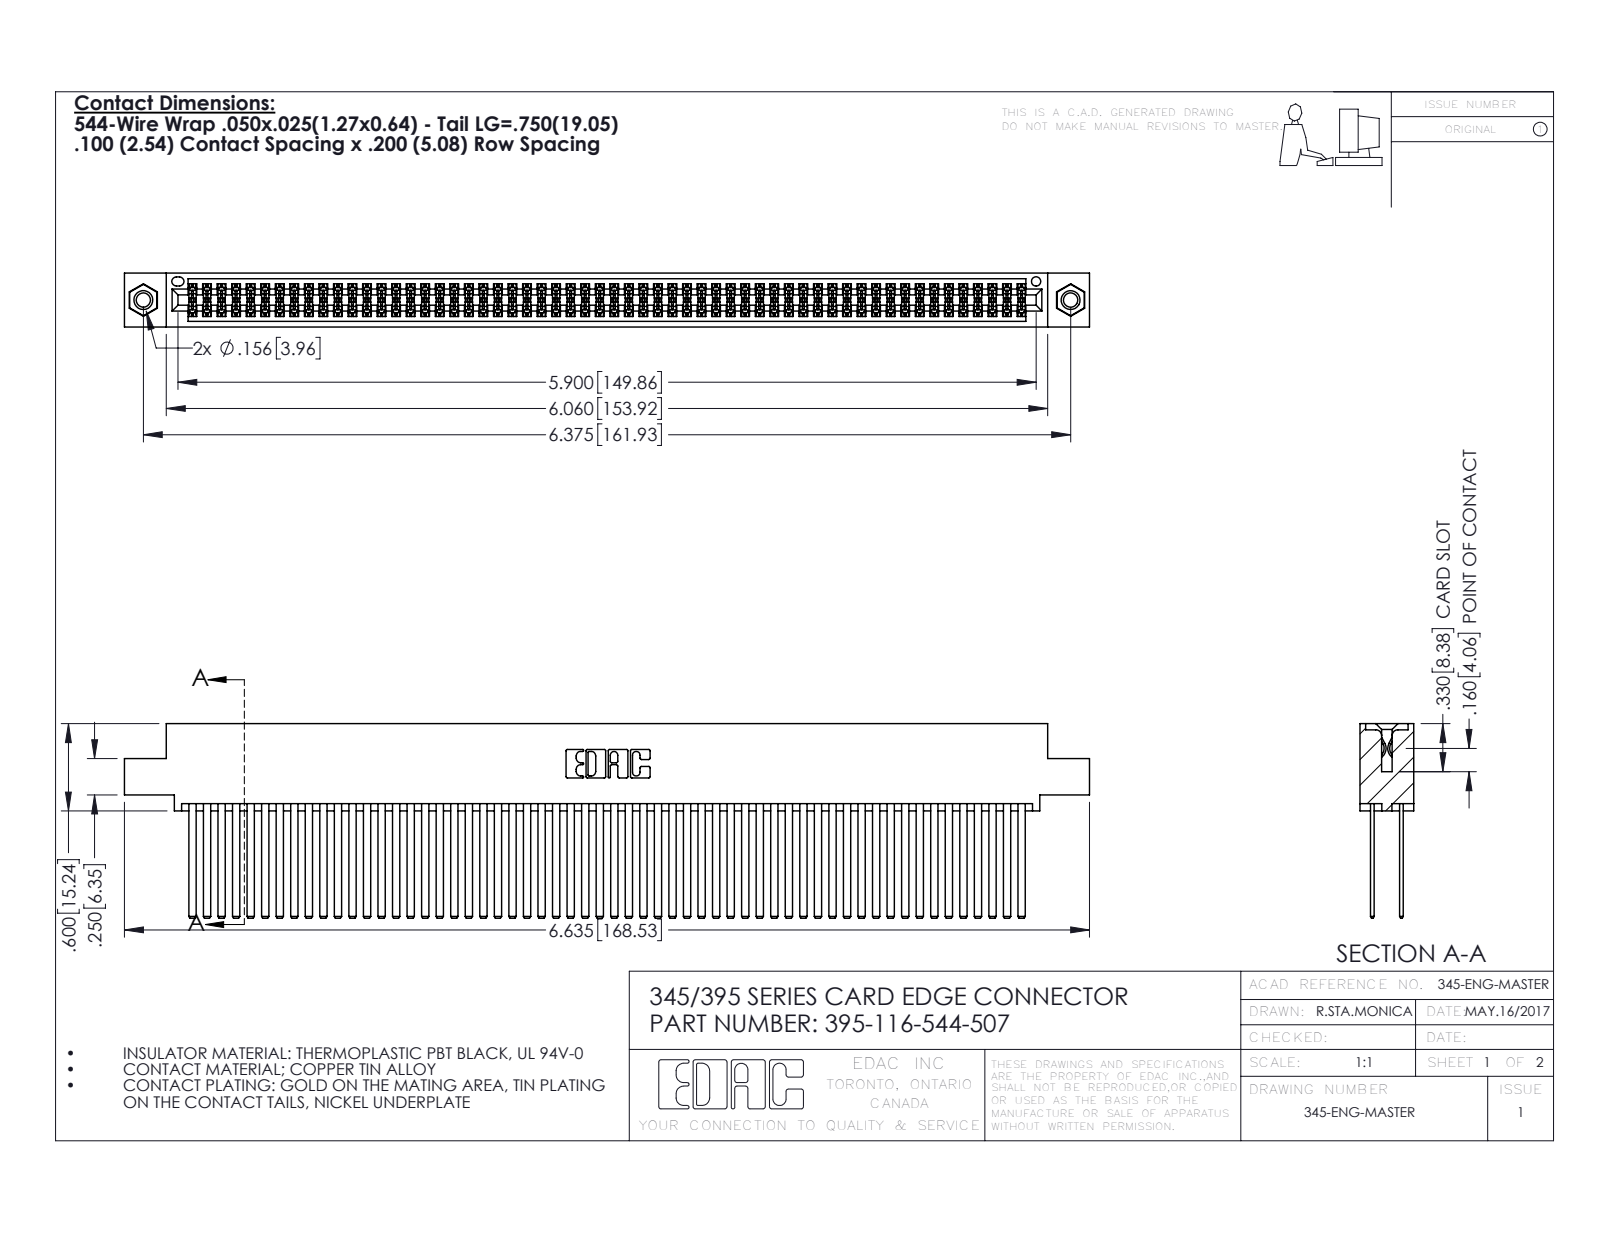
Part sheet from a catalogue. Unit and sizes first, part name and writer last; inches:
Units: inches
Overall size (bounding box): 6.635 × 1.337 × 0.37
Round holes (diameter × count): ⌀0.098 ×2, ⌀0.125 ×2, ⌀0.156 ×2, ⌀0.064 ×1
Round bosses / shafts (diameter × count): ⌀0.155 ×2
Partial cylindrical surfaces — rounded edges, fillets, slot ends (radius × count): R0.006 ×174, R0.01 ×22, R0.007 ×6, R0.031 ×6, R0.026 ×3, R0.014 ×2, R0.019 ×2, R0.022 ×2
Main face-to-face distances: 0.2, 0.025, 0.072, 0.098, 0.272, 0.298, 0.225, 0.175, 0.37, 0.05
Hole centre spacings: 0.27, 6.139, 6.375
Volume: 1.102 in³ · Surface area: 49.43 in²
Bodies: 119 solids, 5294 faces (3480 planar, 1798 cylindrical, 16 other)
Part name (STEP PRODUCT): 395-116-544-507; 345 Part_0.110 Offset - 0.156 Dia-TI; 345-250-001_345-250-005-103; 345-292-001_345-293-144
STEP written by: SolidWorks 2016 (CONFIG_CONTROL_DESIGN)
